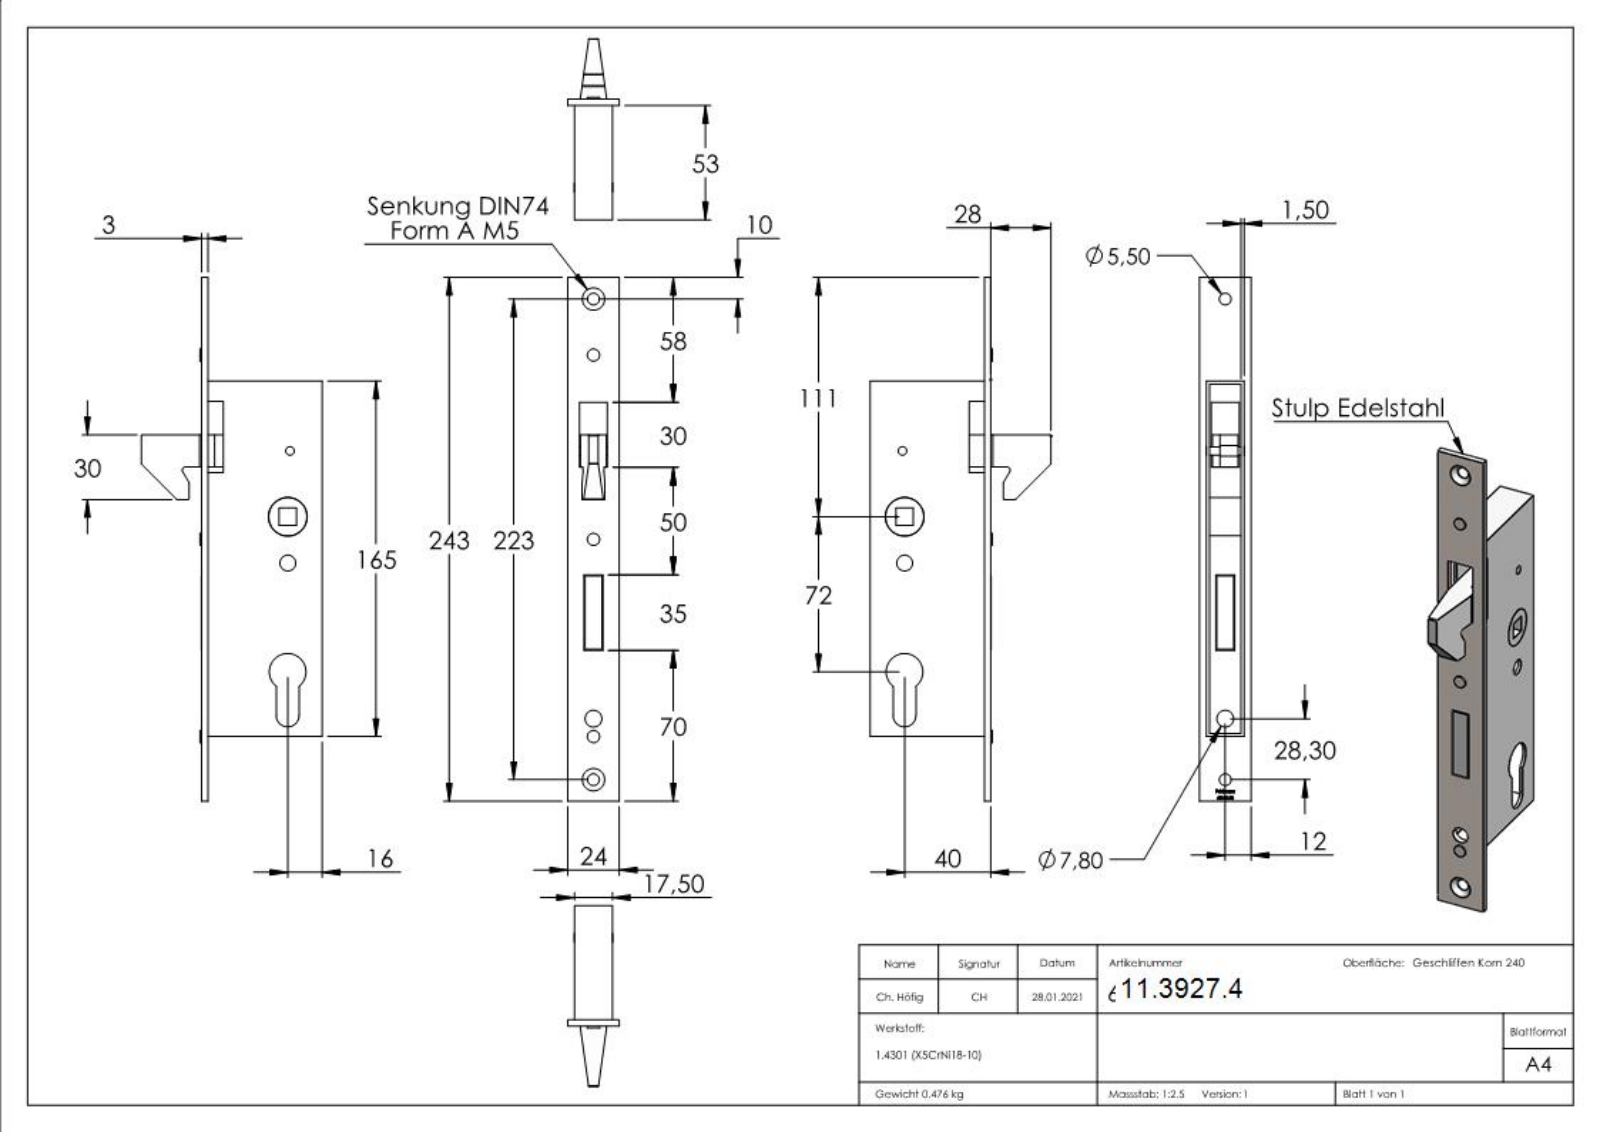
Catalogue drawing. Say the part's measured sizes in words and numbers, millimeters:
The part is named "60109". Its 3-D file was written by "SolidWorks 2015 (CONFIG_CONTROL_DESIGN)". It is 5 solids with 285 faces: 154 planar, 43 cylindrical and 88 other. Overall it measures 243 by 84 by 24 millimeters. Its volume is 60 809 cubic millimeters and its surface area 56 284 square millimeters. Round holes: 2 of diameter 5.5, 1 of diameter 7.4, 1 of diameter 7.8, 1 of diameter 18. Round bosses or shafts: 3 of diameter 5.7, 1 of diameter 17.8, 1 of diameter 4, 1 of diameter 3.8. Partial cylindrical surfaces (rounded edges, fillets, slot ends): 5 of radius 0.5, 1 of radius 1.5, 1 of radius 5.25, 1 of radius 8.5. The main face-to-face distances are 1.5, 16, 14.5, 17.5, 3, 4.75, 163.5, 3.25, 19.25, 20.75. The hole center spacings are 21.5, 28.3, 194.7, 223.
